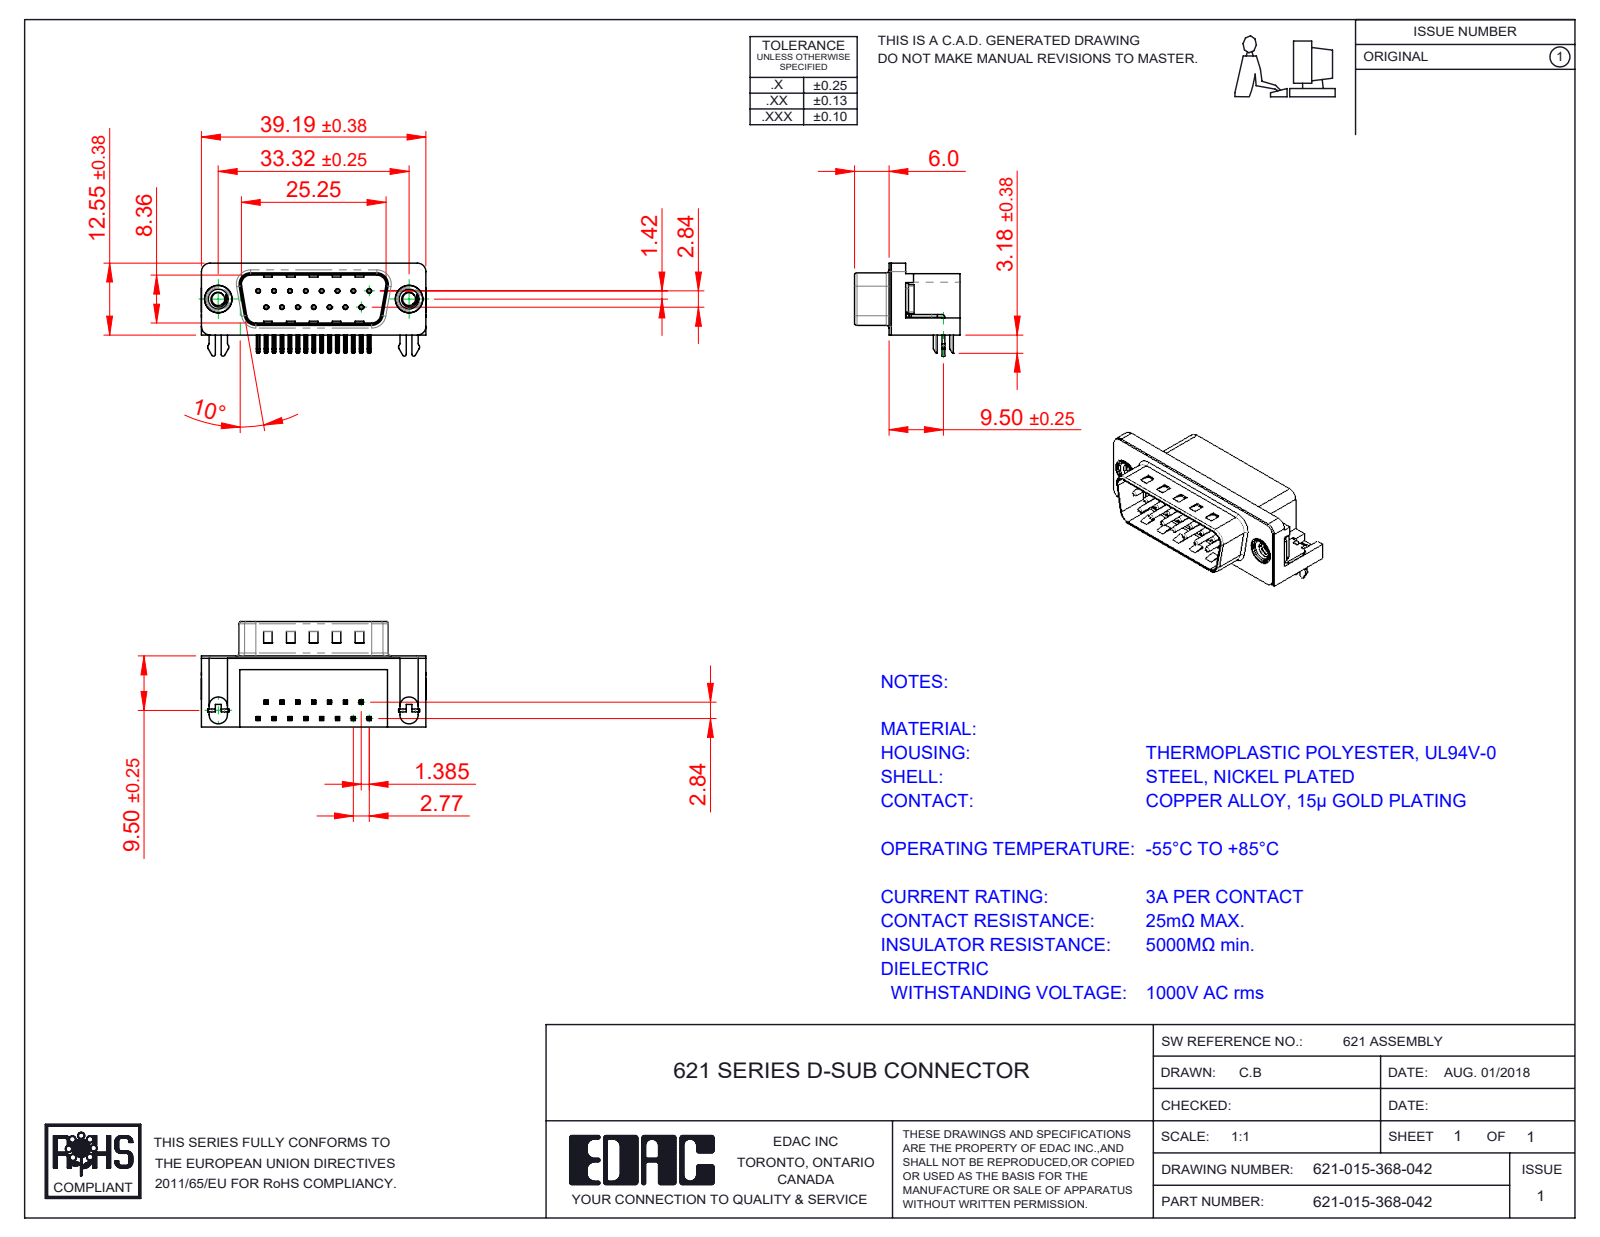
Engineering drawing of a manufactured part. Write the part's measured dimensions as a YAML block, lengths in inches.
part_name: "621 4 Prong Board Lock; 621 4-40 Threaded Rivet; 621 Contact Bottom; 621-015-368-042 (+3 more)"
step_written_by: "SolidWorks 2016 (CONFIG_CONTROL_DESIGN)"
units: inches
bodies: {solids: 21, faces: 1597, planar: 935, cylindrical: 451, other: 211}
overall_size: [1.544, 0.724, 0.64]
volume: 0.27
surface_area: 8.874
round_holes:
  - {diameter: 0.014, count: 15}
  - {diameter: 0.031, count: 15}
  - {diameter: 0.079, count: 2}
  - {diameter: 0.089, count: 2}
  - {diameter: 0.157, count: 2}
  - {diameter: 0.189, count: 2}
  - {diameter: 0.197, count: 2}
round_bosses_or_shafts:
  - {diameter: 0.03, count: 15}
  - {diameter: 0.193, count: 2}
  - {diameter: 0.187, count: 2}
  - {diameter: 0.154, count: 2}
  - {diameter: 0.118, count: 2}
partial_cylinders:
  - {radius: 0.01, count: 72}
  - {radius: 0.005, count: 30}
  - {radius: 0.039, count: 16}
  - {radius: 0.02, count: 9}
  - {radius: 0.063, count: 8}
  - {radius: 0.059, count: 6}
  - {radius: 0.035, count: 4}
  - {radius: 0.079, count: 4}
face_to_face_distances: [0.016, 0.472, 0.407, 0.083, 0.412, 0.488, 0.067, 0.428, 0.345, 0.114]
hole_center_spacings: [0.124, 0.109, 0.218, 0.327, 0.436, 0.198, 0.198, 0.294]
